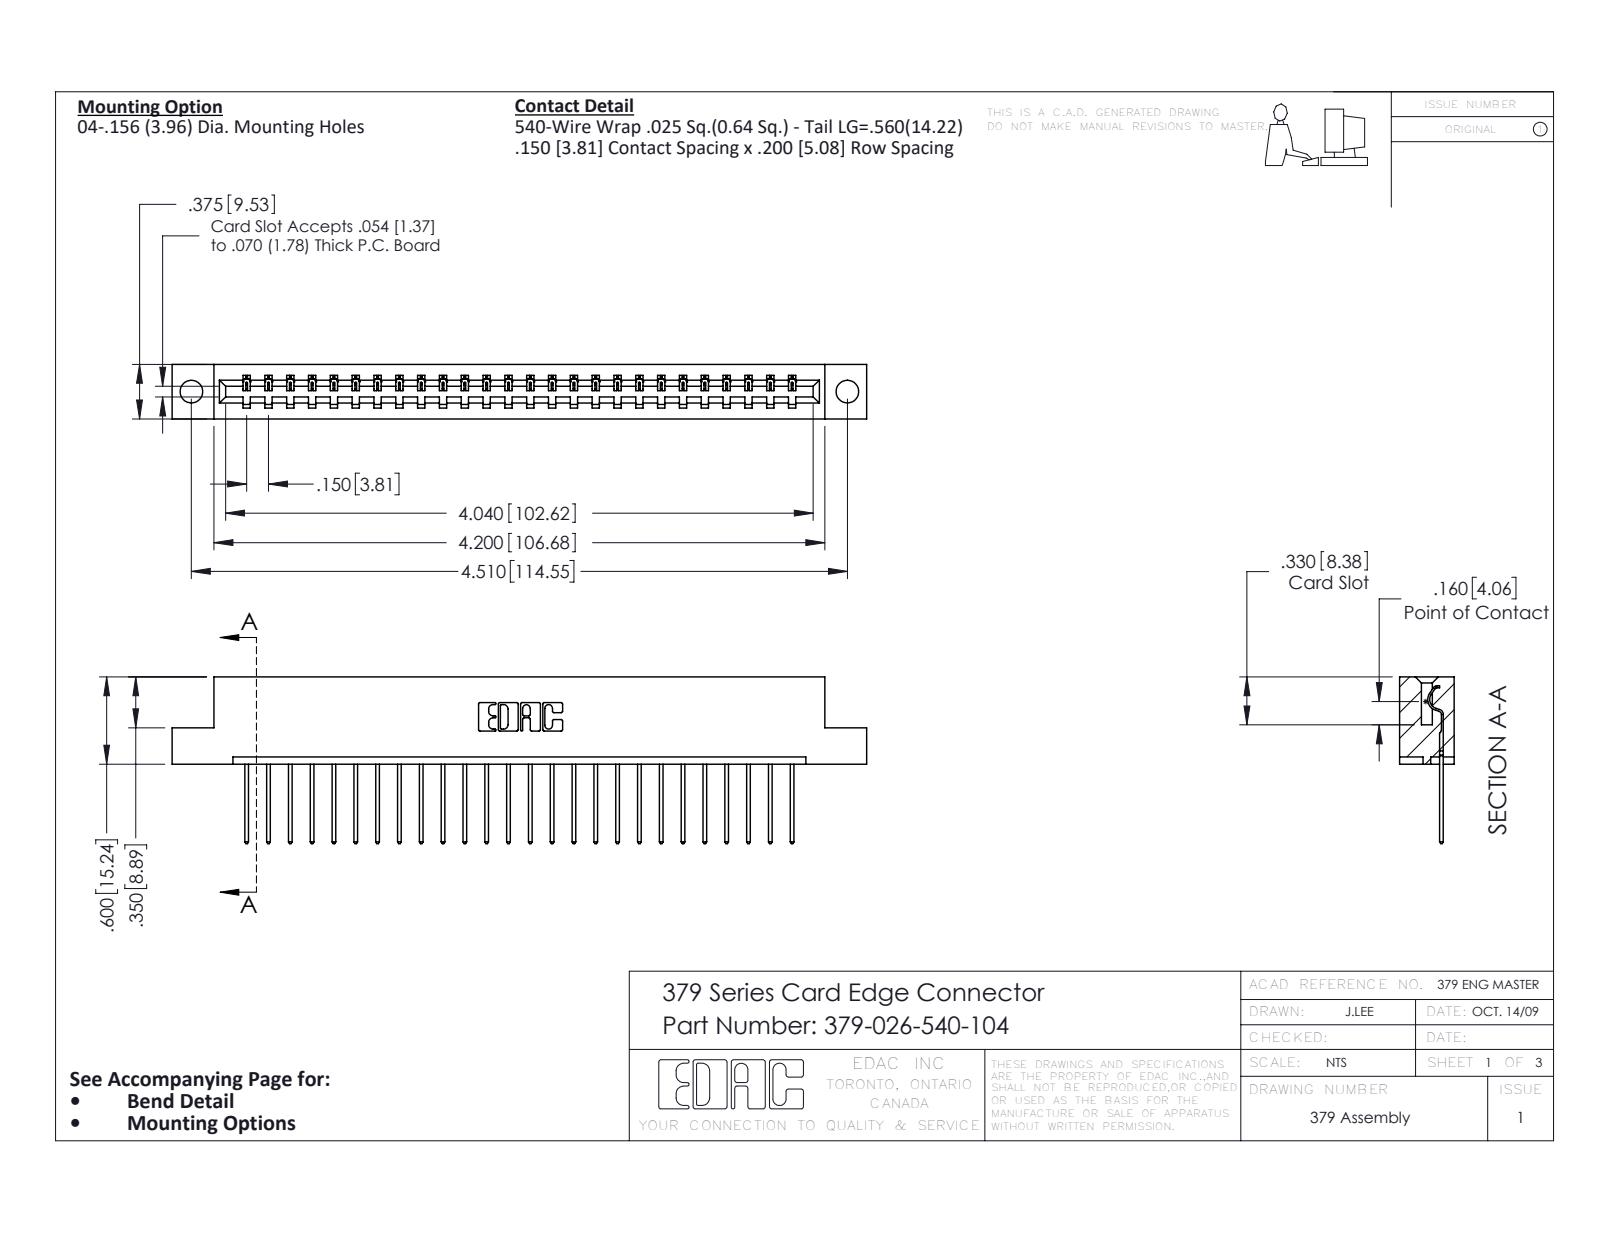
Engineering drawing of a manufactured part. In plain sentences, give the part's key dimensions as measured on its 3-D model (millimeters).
The part is named "345-292-001_345-293-140; 379 Part_Flush - .156 Dia - TH; 379-026-540-104". Its 3-D file was written by "SolidWorks 2016 (CONFIG_CONTROL_DESIGN)". It is 27 solids with 1622 faces: 1162 planar, 460 cylindrical and 0 other. Overall it measures 121.3 by 29.1 by 9.5 millimeters. Its volume is 12 500 cubic millimeters and its surface area 12 770 square millimeters. Round holes: 2 of diameter 4. Partial cylindrical surfaces (rounded edges, fillets, slot ends): 52 of radius 0.2, 52 of radius 0.3, 22 of radius 0.3, 6 of radius 0.2, 6 of radius 0.8, 3 of radius 0.7, 1 of radius 0.4, 1 of radius 0.6. The main face-to-face distances are 7.6, 1.9, 9.5, 5.7, 15.2, 5.1, 7, 2.5, 0.6, 3.8. The hole center spacings are 114.6.
